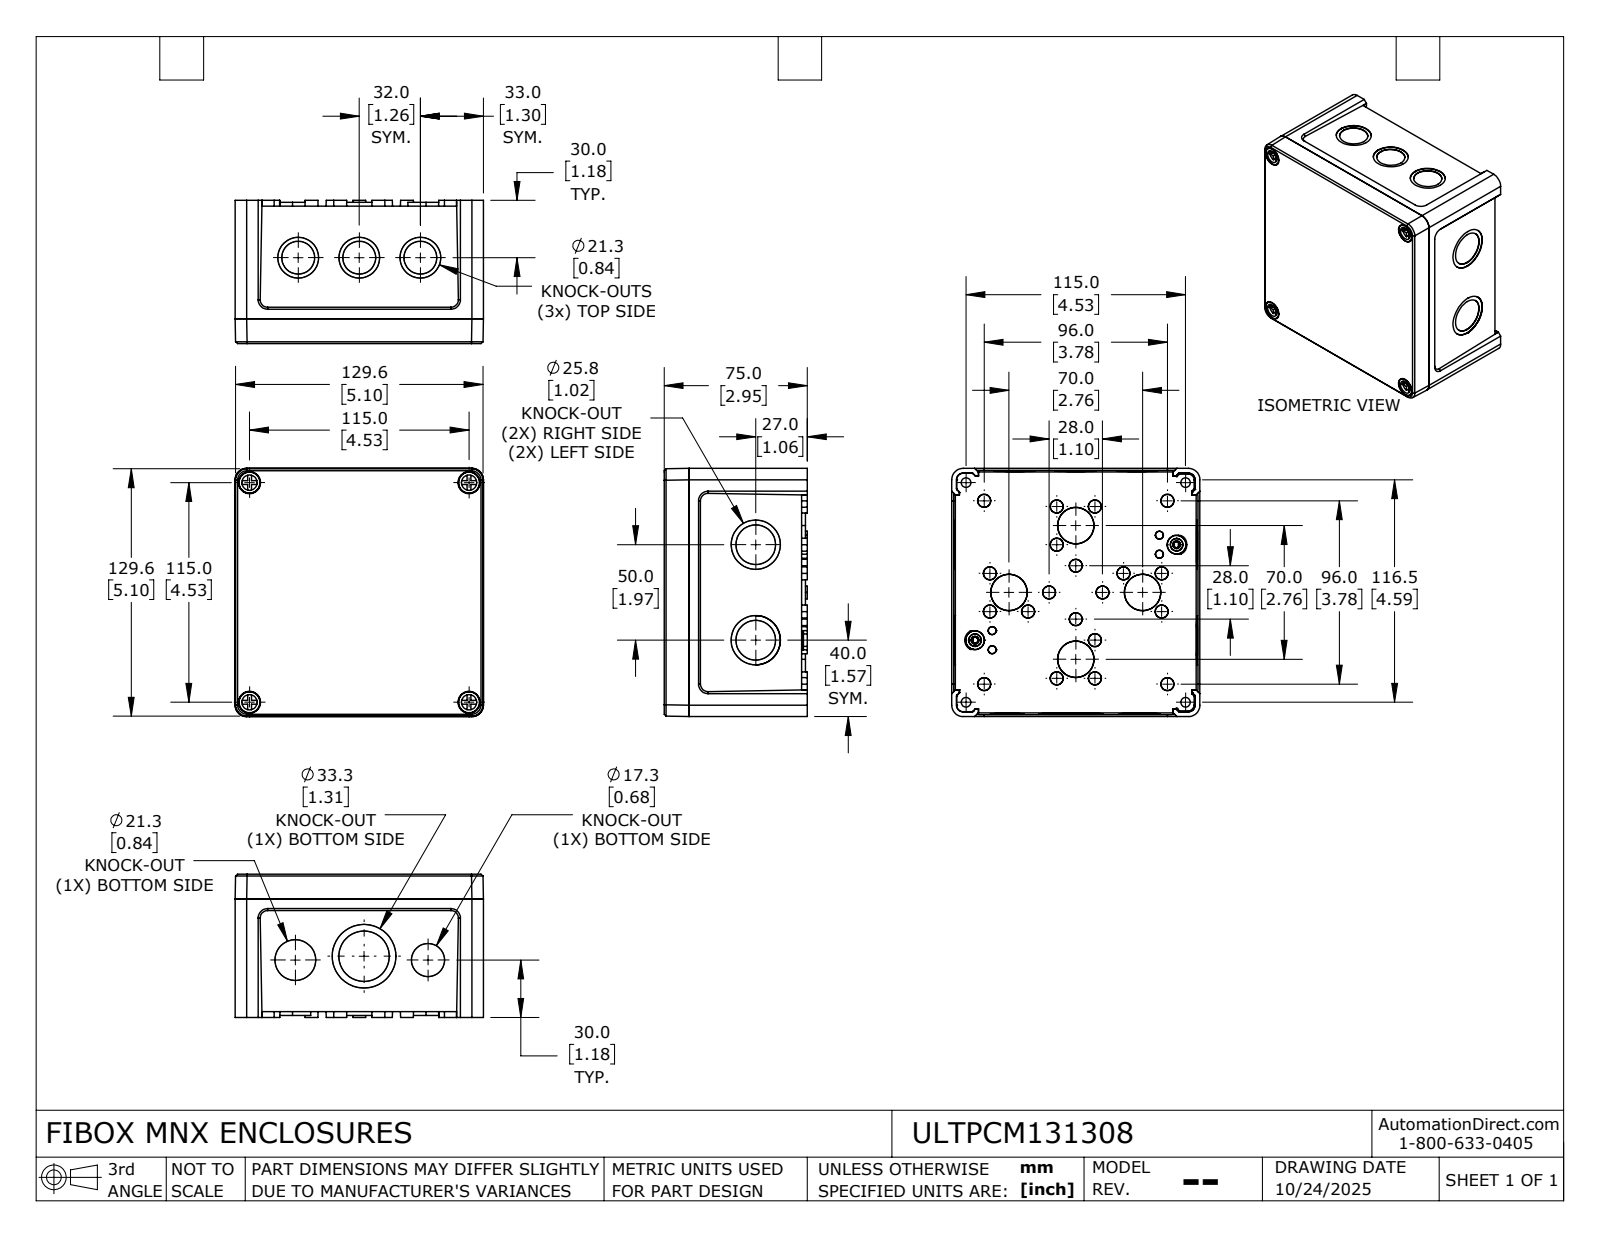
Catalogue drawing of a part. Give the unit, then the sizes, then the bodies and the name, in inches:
Units: inches
Overall size (bounding box): 5.118 × 5.118 × 2.953
Round holes (diameter × count): ⌀0.126 ×20, ⌀0.197 ×4, ⌀0.295 ×4, ⌀0.315 ×4, ⌀0.561 ×4, ⌀0.84 ×4, ⌀0.677 ×3, ⌀0.819 ×2, ⌀0.846 ×2, ⌀1.016 ×2, ⌀0.683 ×1, ⌀1.039 ×1
Round bosses / shafts (diameter × count): ⌀0.433 ×4, ⌀0.283 ×4
Partial cylindrical surfaces — rounded edges, fillets, slot ends (radius × count): R0.02 ×39, R0.039 ×8, R0.079 ×8, R0.108 ×8, R0.236 ×8, R0.197 ×4
Main face-to-face distances: 0.081, 2.835, 2.726, 0.108, 2.559, 0.276, 2.451, 5, 5.081, 0.512
Hole centre spacings: 0.557, 1.949, 2.027, 2.567, 0.787, 1.282, 1.484, 1.499
Volume: 16.38 in³ · Surface area: 234.9 in²
Bodies: 6 solids, 712 faces (298 planar, 214 cylindrical, 200 other)
Part name (STEP PRODUCT): ULTPCM131308_Default
STEP written by: SolidWorks 2024 (CONFIG_CONTROL_DESIGN)
